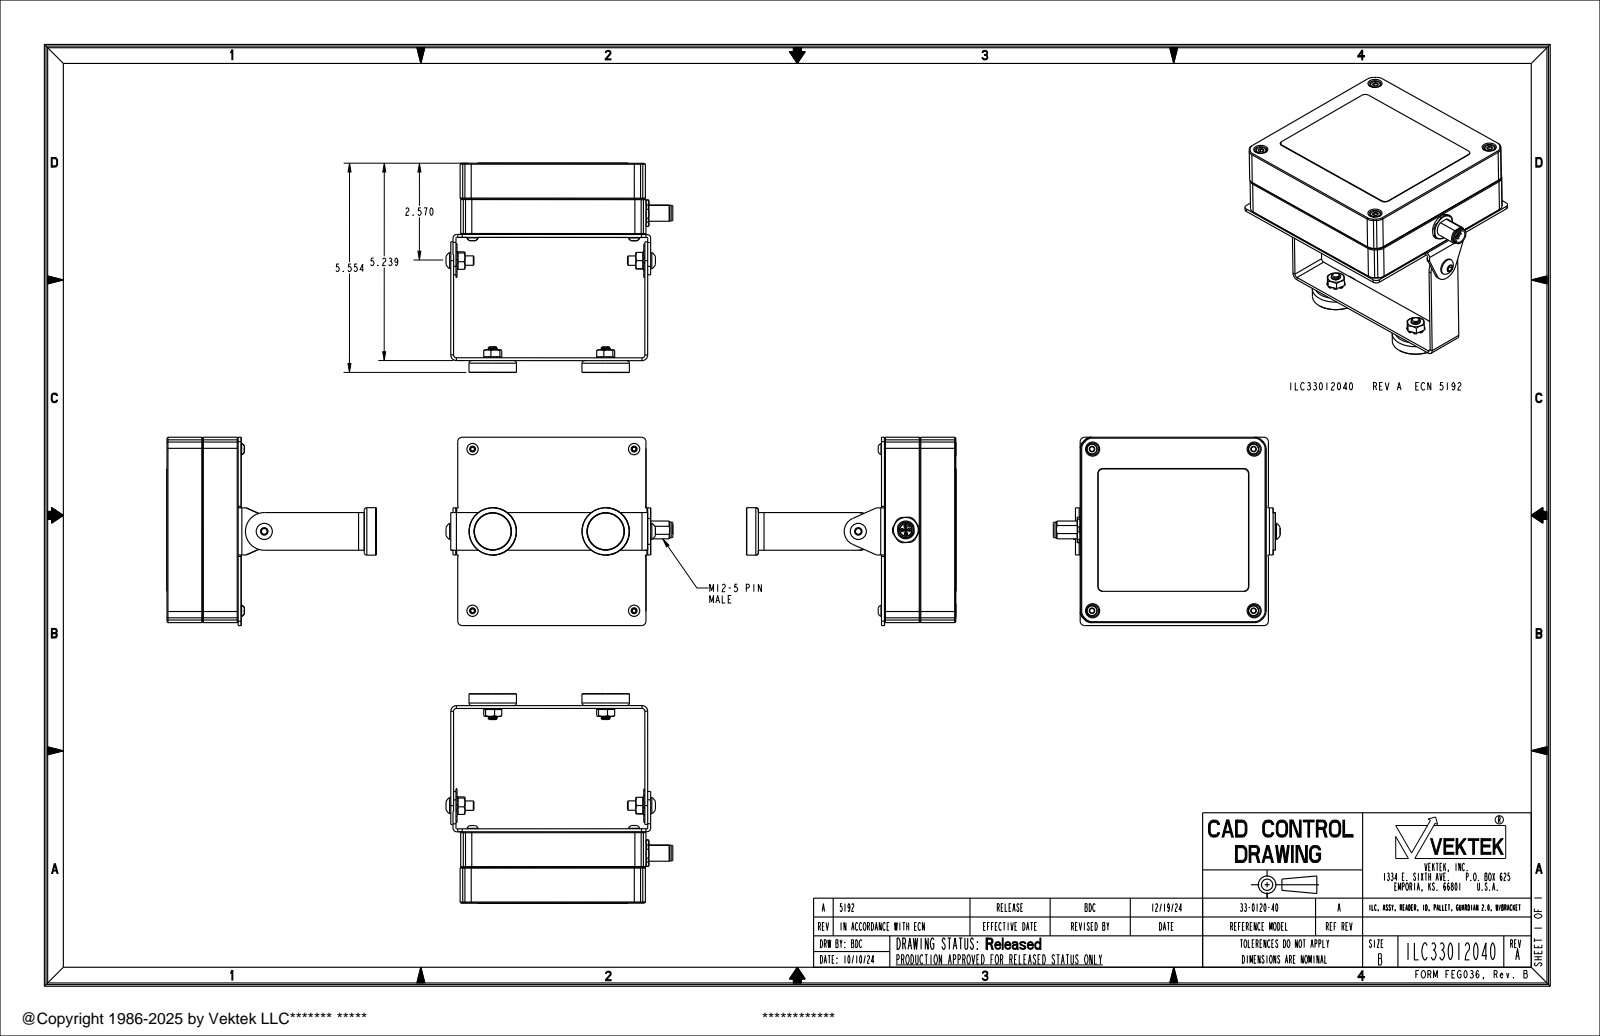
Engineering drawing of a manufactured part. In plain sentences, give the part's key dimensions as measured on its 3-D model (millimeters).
The part is named "ILC33012040". Its 3-D file was written by "CREO PARAMETRIC BY PTC INC, 2021164 (AUTOMOTIVE_DESIGN)". It is 1 solid with 955 faces: 526 planar, 269 cylindrical and 160 other. Overall it measures 152.6 by 143.1 by 127 millimeters. Its volume is 814 600 cubic millimeters and its surface area 81 290 square millimeters. Round holes: 5 of diameter 2.2, 4 of diameter 6.8, 4 of diameter 8.3, 3 of diameter 7.1, 2 of diameter 5.2. Round bosses or shafts: 5 of diameter 1, 4 of diameter 7.6, 4 of diameter 7, 4 of diameter 6.4, 2 of diameter 32, 2 of diameter 10.9, 1 of diameter 10.7, 1 of diameter 10.3. Partial cylindrical surfaces (rounded edges, fillets, slot ends): 16 of radius 6, 4 of radius 3, 4 of radius 3.3, 4 of radius 3.3, 4 of radius 4.7, 4 of radius 6.1, 2 of radius 0.5, 2 of radius 1.9. The main face-to-face distances are 50.2, 50, 0.4, 125, 1.9, 131.4, 131.2, 81.2, 125, 124.6. The hole center spacings are 3.5, 2.5, 2.5, 5, 109, 109, 3.5, 29.6.
